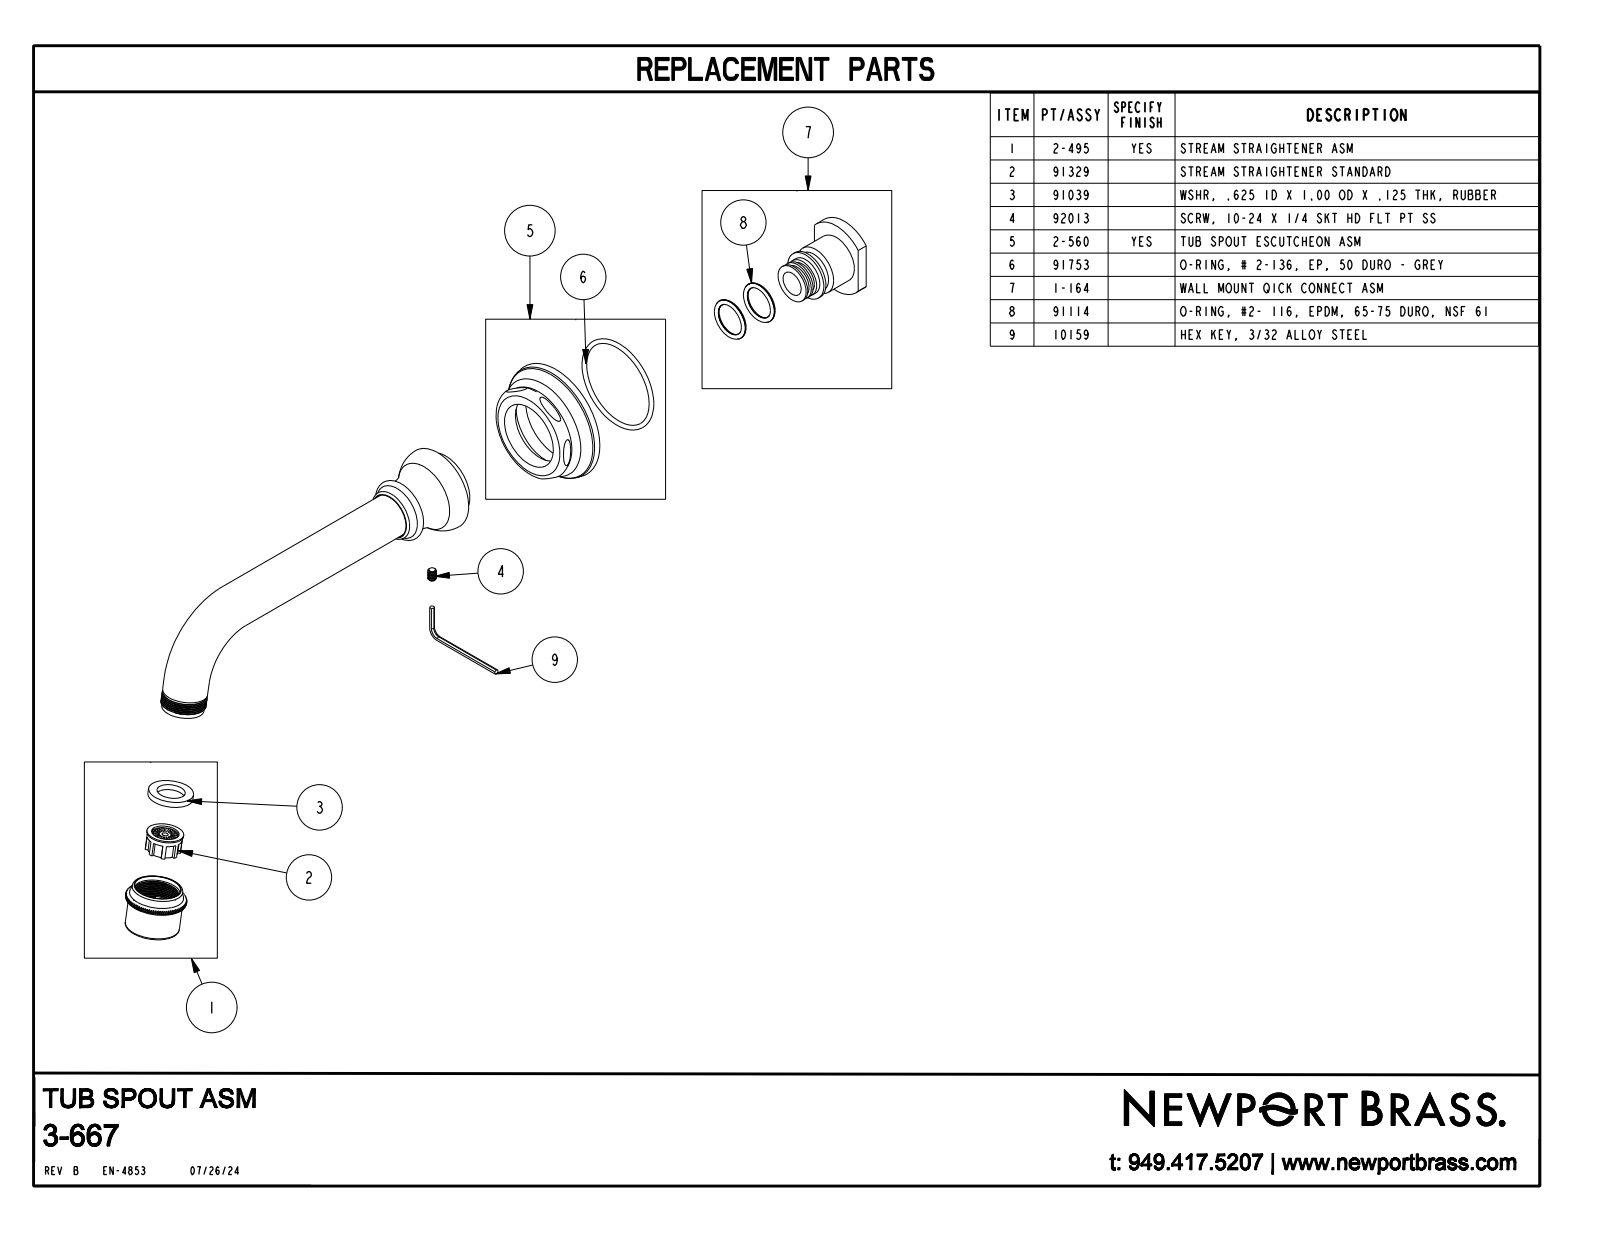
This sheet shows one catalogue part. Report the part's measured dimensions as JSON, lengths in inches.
{"part_name": "3-667", "step_written_by": "CREO PARAMETRIC BY PTC INC, 2018400 (AUTOMOTIVE_DESIGN)", "units": "inches", "bodies": {"solids": 1, "faces": 44, "planar": 6, "cylindrical": 6, "other": 32}, "overall_size": [9.455, 3.915, 2.74], "volume_in3": 13.05, "surface_area_in2": 49.43, "round_bosses_or_shafts": [[1, 2], [1.2, 1]], "face_to_face_distances": [2.34, 1]}
